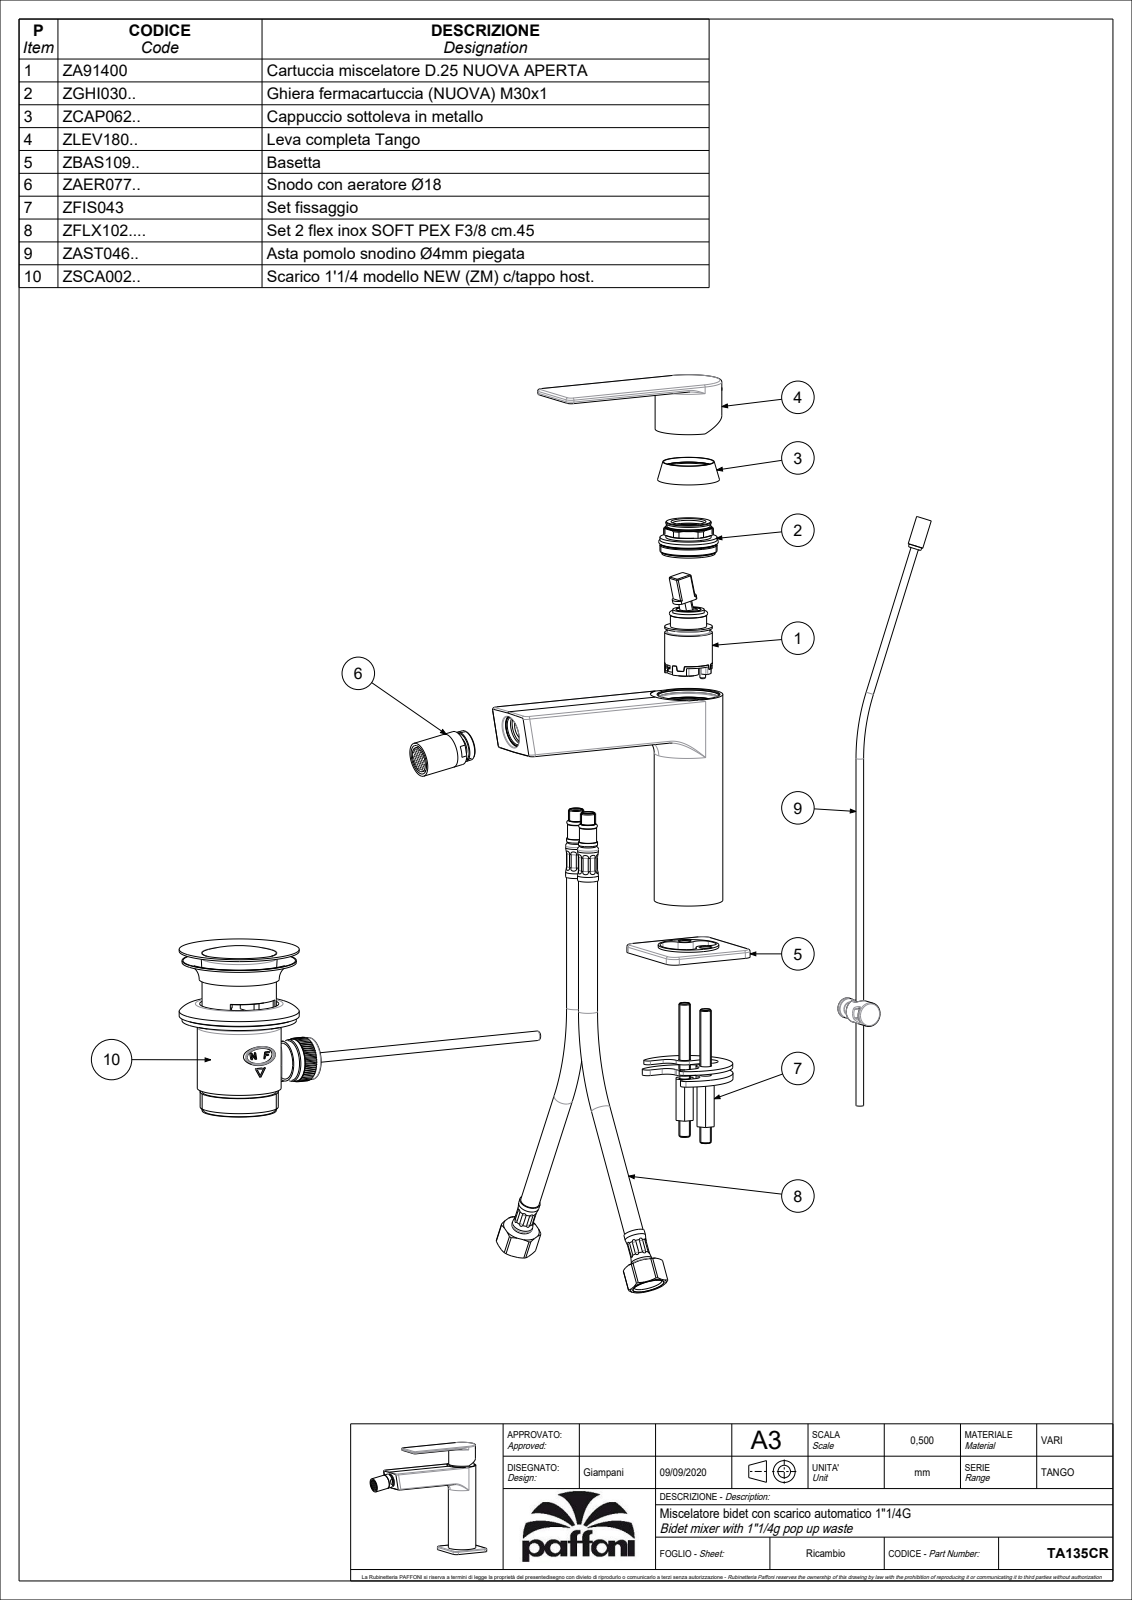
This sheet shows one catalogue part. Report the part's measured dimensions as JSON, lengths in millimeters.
{"part_name": "TA135CR", "step_written_by": "CREO PARAMETRIC BY PTC INC, 2020044 (CONFIG_CONTROL_DESIGN)", "units": "millimeters", "bodies": {"solids": 0, "faces": 110, "planar": 30, "cylindrical": 46, "other": 34}, "overall_size": [171.84, 141.2, 50], "round_holes": [[5, 1]], "round_bosses_or_shafts": [[36, 1], [35, 1], [18, 1], [10, 1], [8, 1], [7.6, 1], [4, 1]], "partial_cylinders_radius": [[1, 10], [1.2, 8], [3, 4], [5, 4], [0.8, 2]], "face_to_face_distances": [22, 141.2, 4, 137.2, 3, 138.2, 134.2, 36, 113.7, 109.7]}
